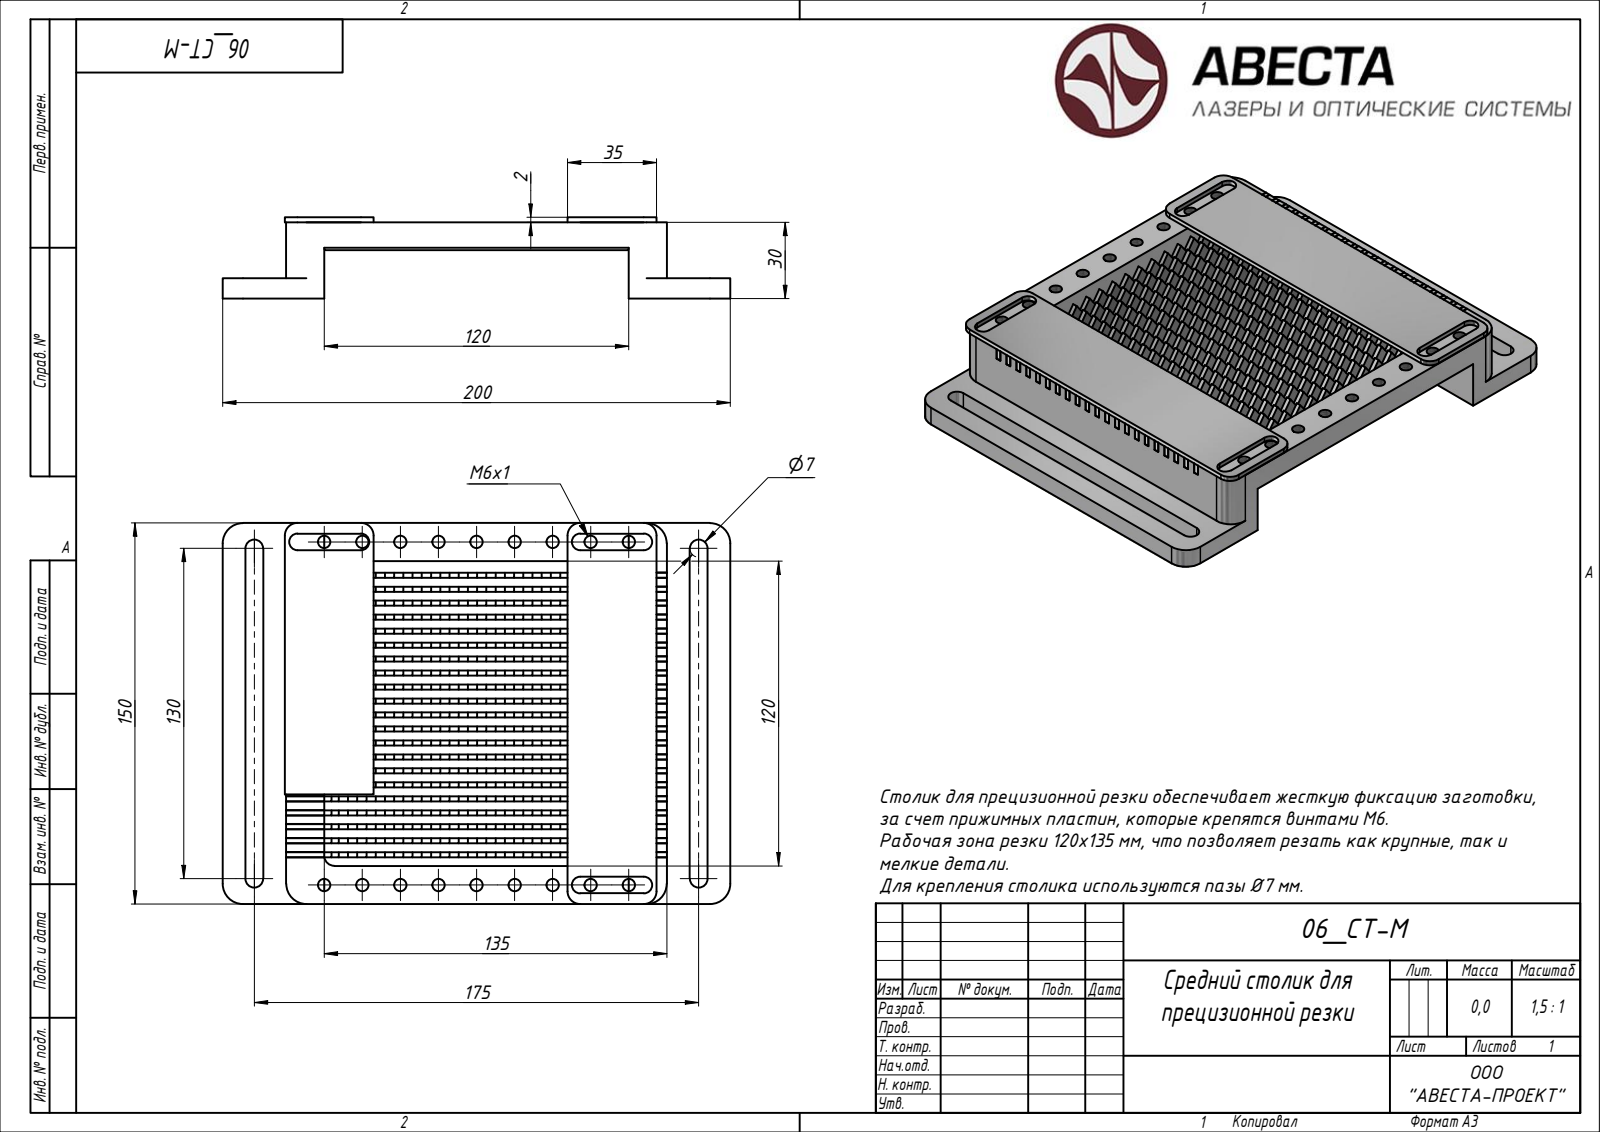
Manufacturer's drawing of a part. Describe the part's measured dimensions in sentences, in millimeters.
The part is named "Столик для резки_Shrinkwrap_1". Its 3-D file was written by "Autodesk Inventor 2020 (AUTOMOTIVE_DESIGN)". It is 1 solid with 889 faces: 829 planar, 60 cylindrical and 0 other. Overall it measures 200 by 150 by 32 millimeters. Its volume is 248 469 cubic millimeters and its surface area 118 238 square millimeters. Round holes: 28 of diameter 4.13. Partial cylindrical surfaces (rounded edges, fillets, slot ends): 12 of radius 8, 8 of radius 2.25, 8 of radius 5, 4 of radius 3.5. The main face-to-face distances are 11, 2, 15, 9, 24, 30, 32, 5.5, 135, 16.5. The hole center spacings are 10, 135.37, 20, 136.47, 30, 138.29, 40, 140.8.
